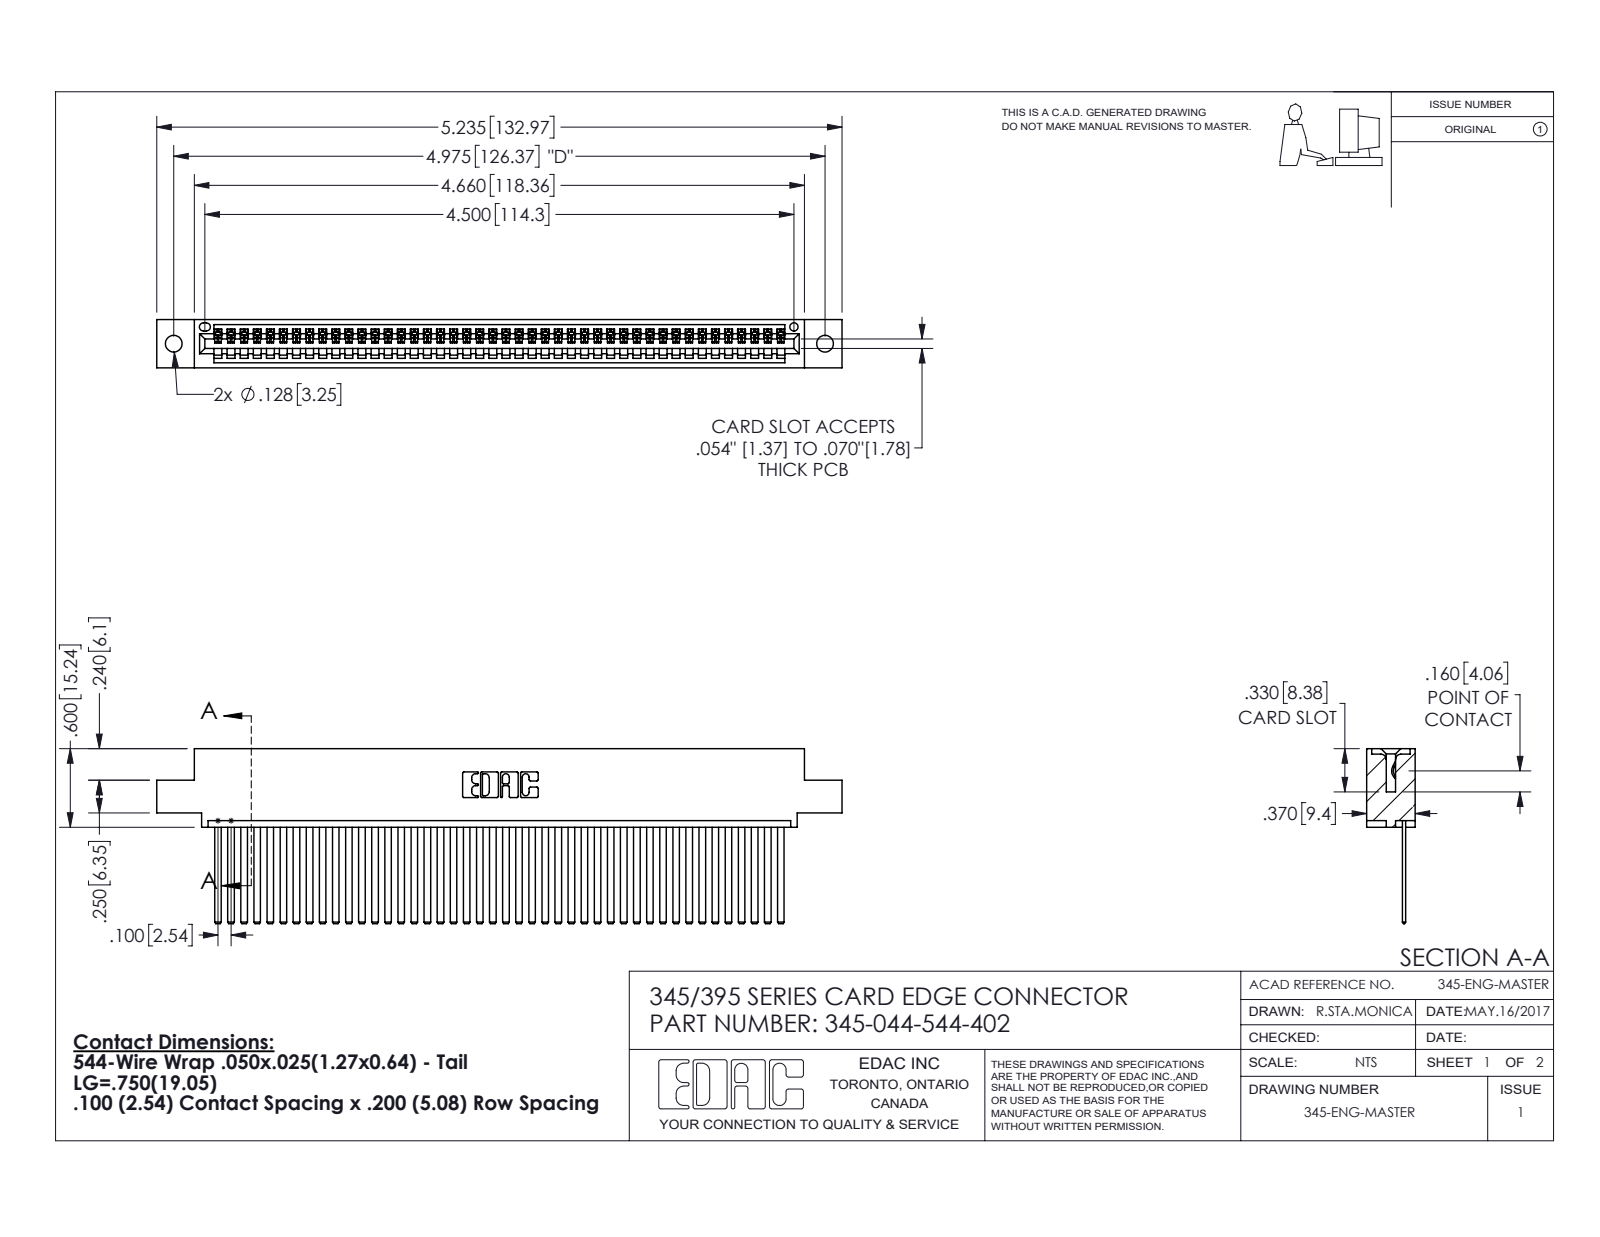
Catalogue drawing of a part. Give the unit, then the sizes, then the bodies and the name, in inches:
Units: inches
Overall size (bounding box): 5.235 × 1.337 × 0.37
Round holes (diameter × count): ⌀0.128 ×2, ⌀0.064 ×1
Partial cylindrical surfaces — rounded edges, fillets, slot ends (radius × count): R0.006 ×88, R0.01 ×22, R0.007 ×6, R0.031 ×6, R0.026 ×3, R0.031 ×2, R0.04 ×2, R0.014 ×1
Main face-to-face distances: 0.072, 0.298, 0.025, 0.098, 0.272, 0.37, 0.2, 0.225, 0.149, 0.072
Hole centre spacings: 0.27, 4.739, 4.975
Volume: 0.796 in³ · Surface area: 28.99 in²
Bodies: 45 solids, 2418 faces (1668 planar, 750 cylindrical, 0 other)
Part name (STEP PRODUCT): 345-044-544-402; 345-292-001_345-293-144; 345 Part_0.110 Offset - 0.128 Dia
STEP written by: SolidWorks 2016 (CONFIG_CONTROL_DESIGN)
